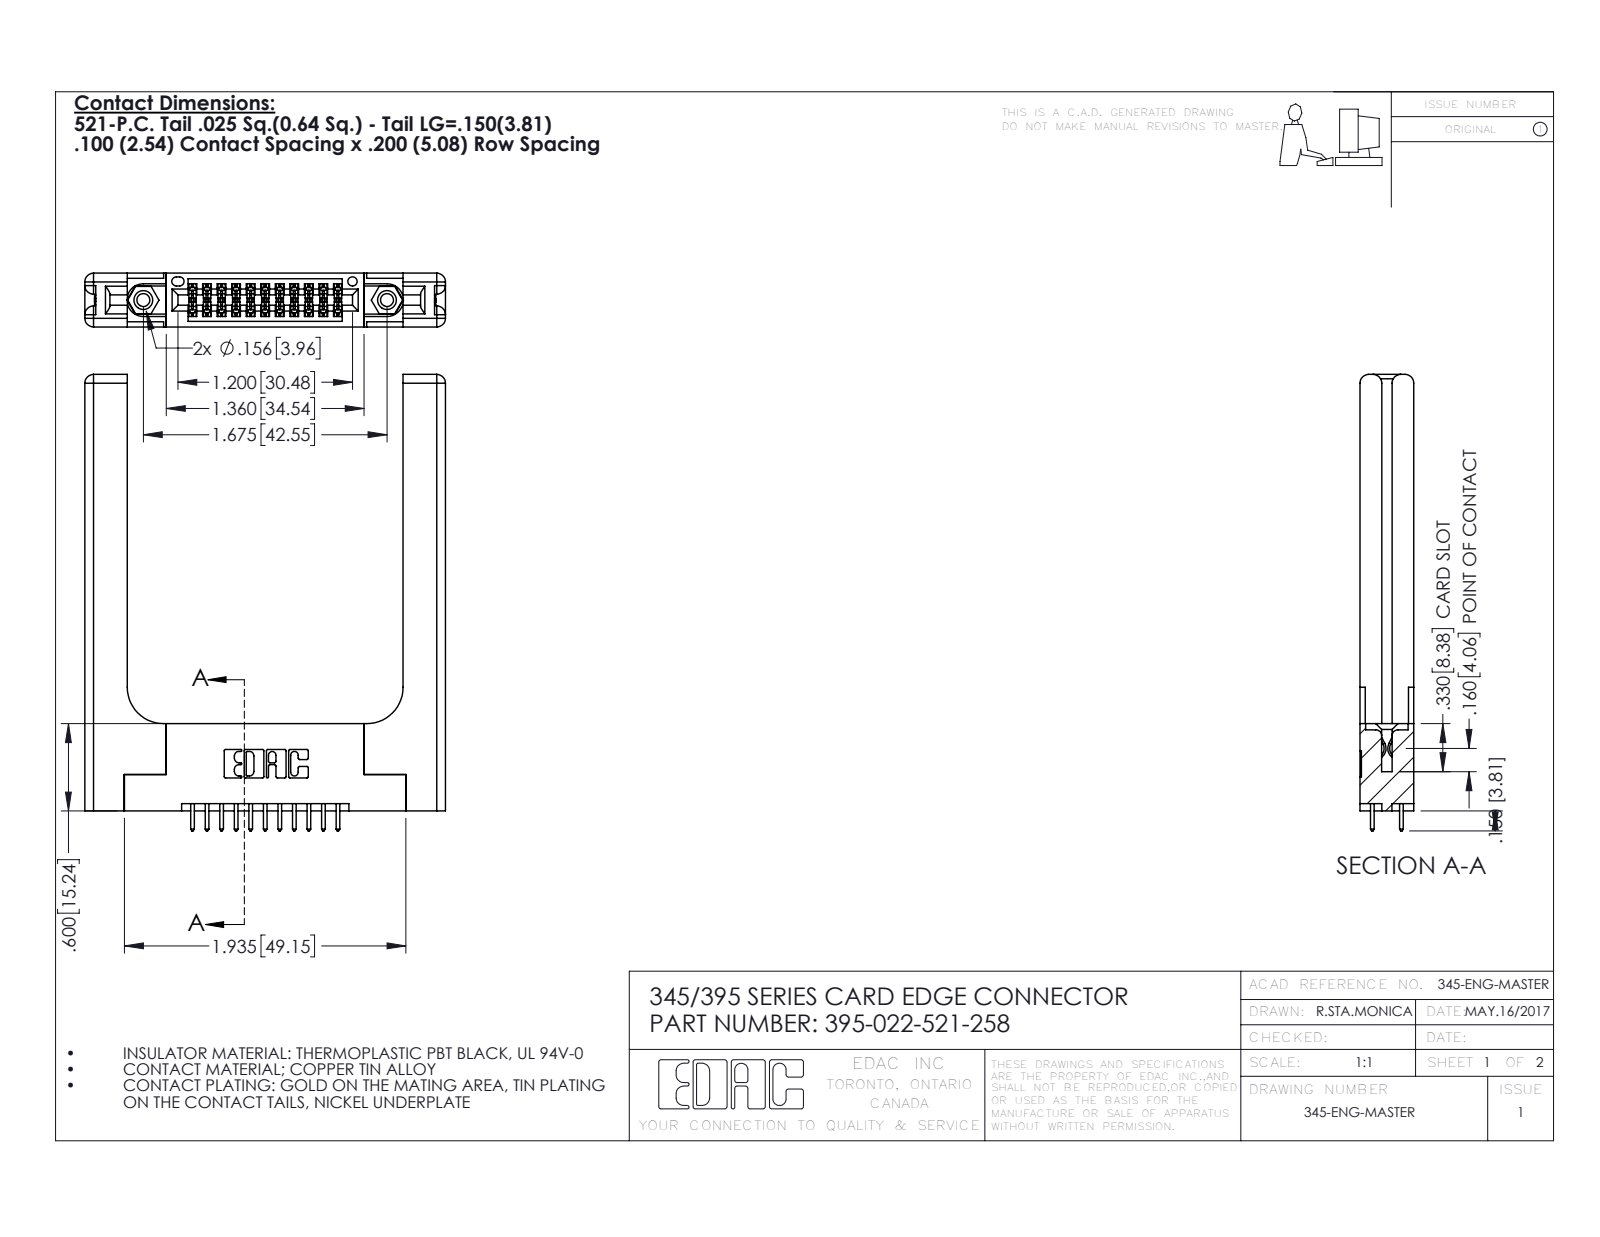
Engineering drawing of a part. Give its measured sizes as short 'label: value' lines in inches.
name: 345-292-001_345-293-121; 345 Part_Flush Mounting Lugs - 0.156 Dia-TH; 345-220-058_345-220-058; 395-022-521-258 (+1 more)
written by: SolidWorks 2016 (CONFIG_CONTROL_DESIGN)
unit: in
bodies: 27 solids, 1482 faces (954 planar, 468 cylindrical, 60 other)
size: 3.137 × 2.479 × 0.37
volume: 0.872 in³; area: 20.15 in²
holes: 2× ⌀0.089, 2× ⌀0.125, 2× ⌀0.156, 1× ⌀0.064
bosses: 2× ⌀0.155
rounds: 33× R0.006, 22× R0.01, 22× R0.01, 16× R0.06, 6× R0.007, 6× R0.031, 3× R0.026, 2× R0.014
face distances: 0.37, 0.072, 0.077, 0.148, 0.15, 0.298, 0.22, 0.2, 0.225, 1.896
hole spacings: 0.27, 1.443, 1.675
